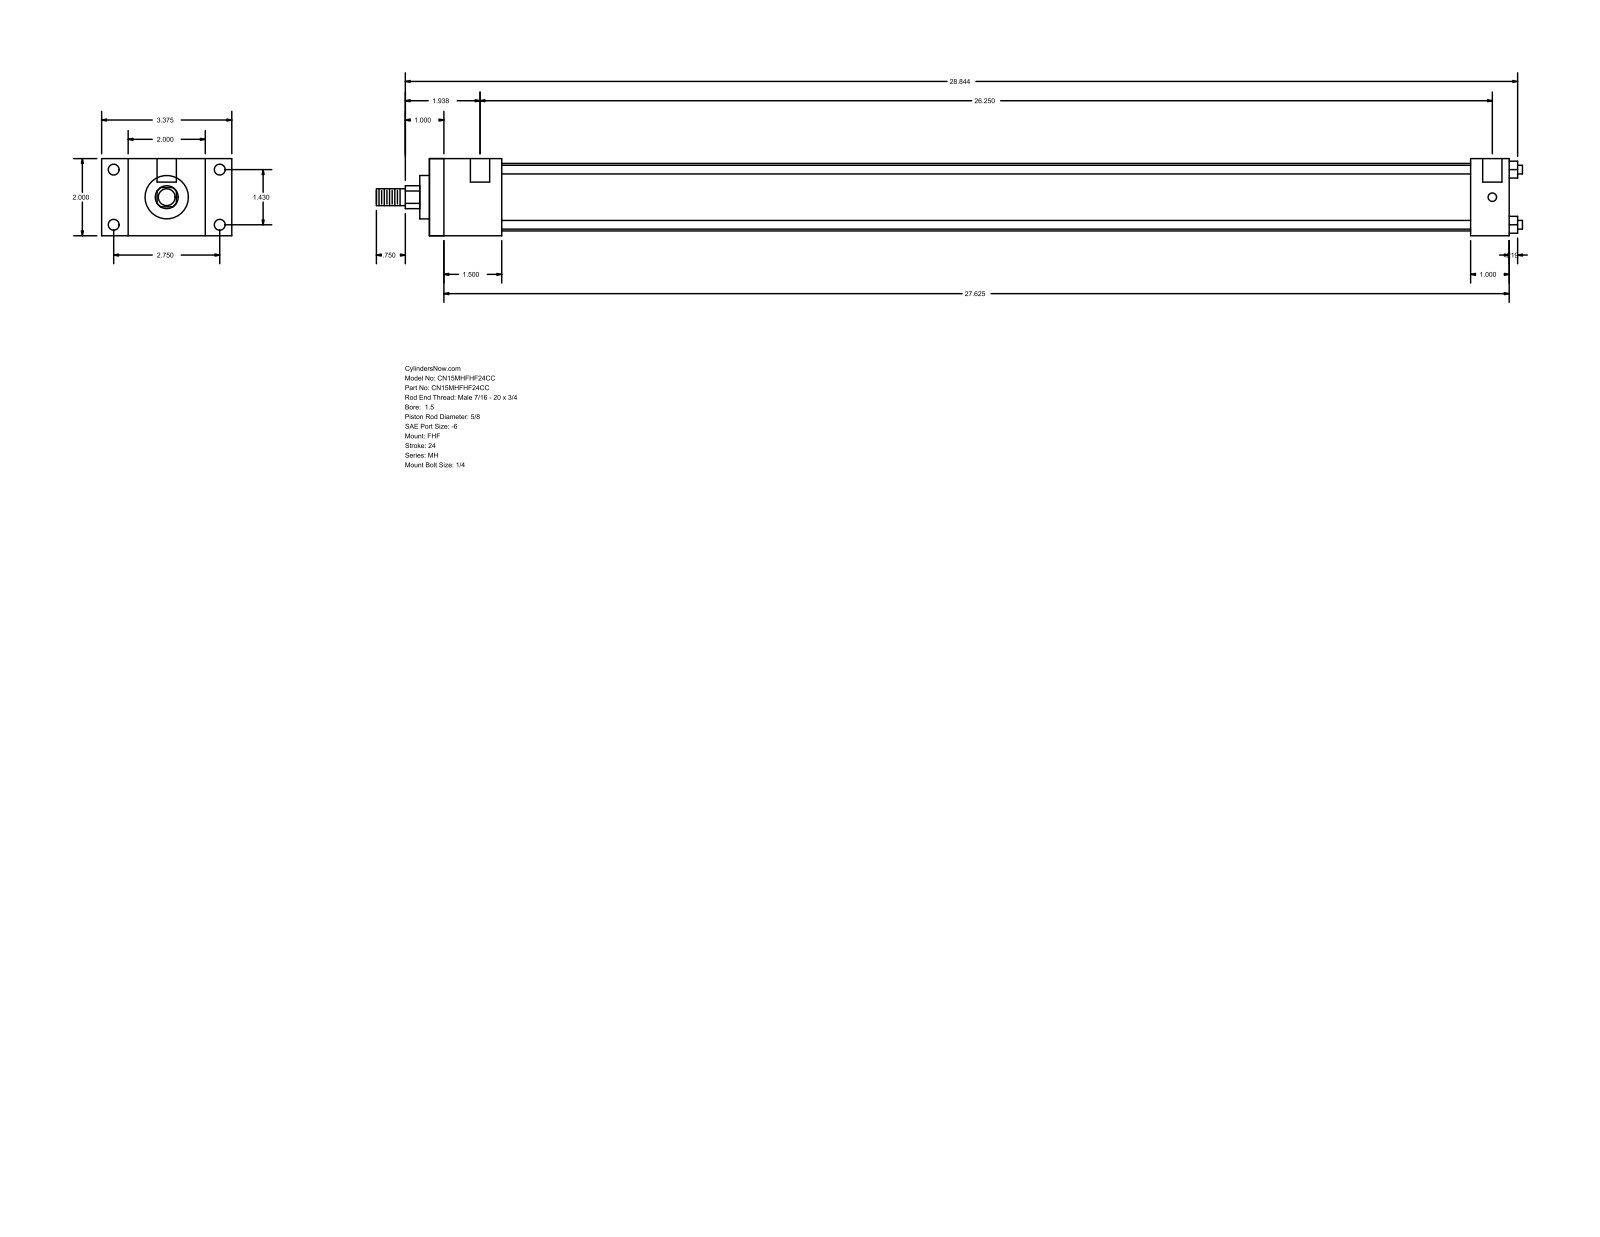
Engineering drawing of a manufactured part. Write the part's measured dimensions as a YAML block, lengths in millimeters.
part_name: "MH_FHF__0150_0.625"
step_written_by: "GSSL Pune (CONFIG_CONTROL_DESIGN)"
units: millimeters
bodies: {solids: 0, faces: 88, planar: 60, cylindrical: 28, other: 0}
overall_size: [754.86, 85.72, 50.8]
round_holes:
  - {diameter: 5.56, count: 4}
  - {diameter: 7.14, count: 4}
  - {diameter: 12.7, count: 2}
round_bosses_or_shafts:
  - {diameter: 5.71, count: 4}
  - {diameter: 44.45, count: 1}
  - {diameter: 28.57, count: 1}
  - {diameter: 15.88, count: 1}
  - {diameter: 11.11, count: 1}
partial_cylinders:
  - {radius: 7.54, count: 1}
face_to_face_distances: [50.8, 17.46, 68.26, 47.62, 85.72, 711.2, 663.58, 685.79, 638.17, 25.41]
hole_center_spacings: [36.32, 69.84, 78.72, 669.92, 3.17, 666.75]
